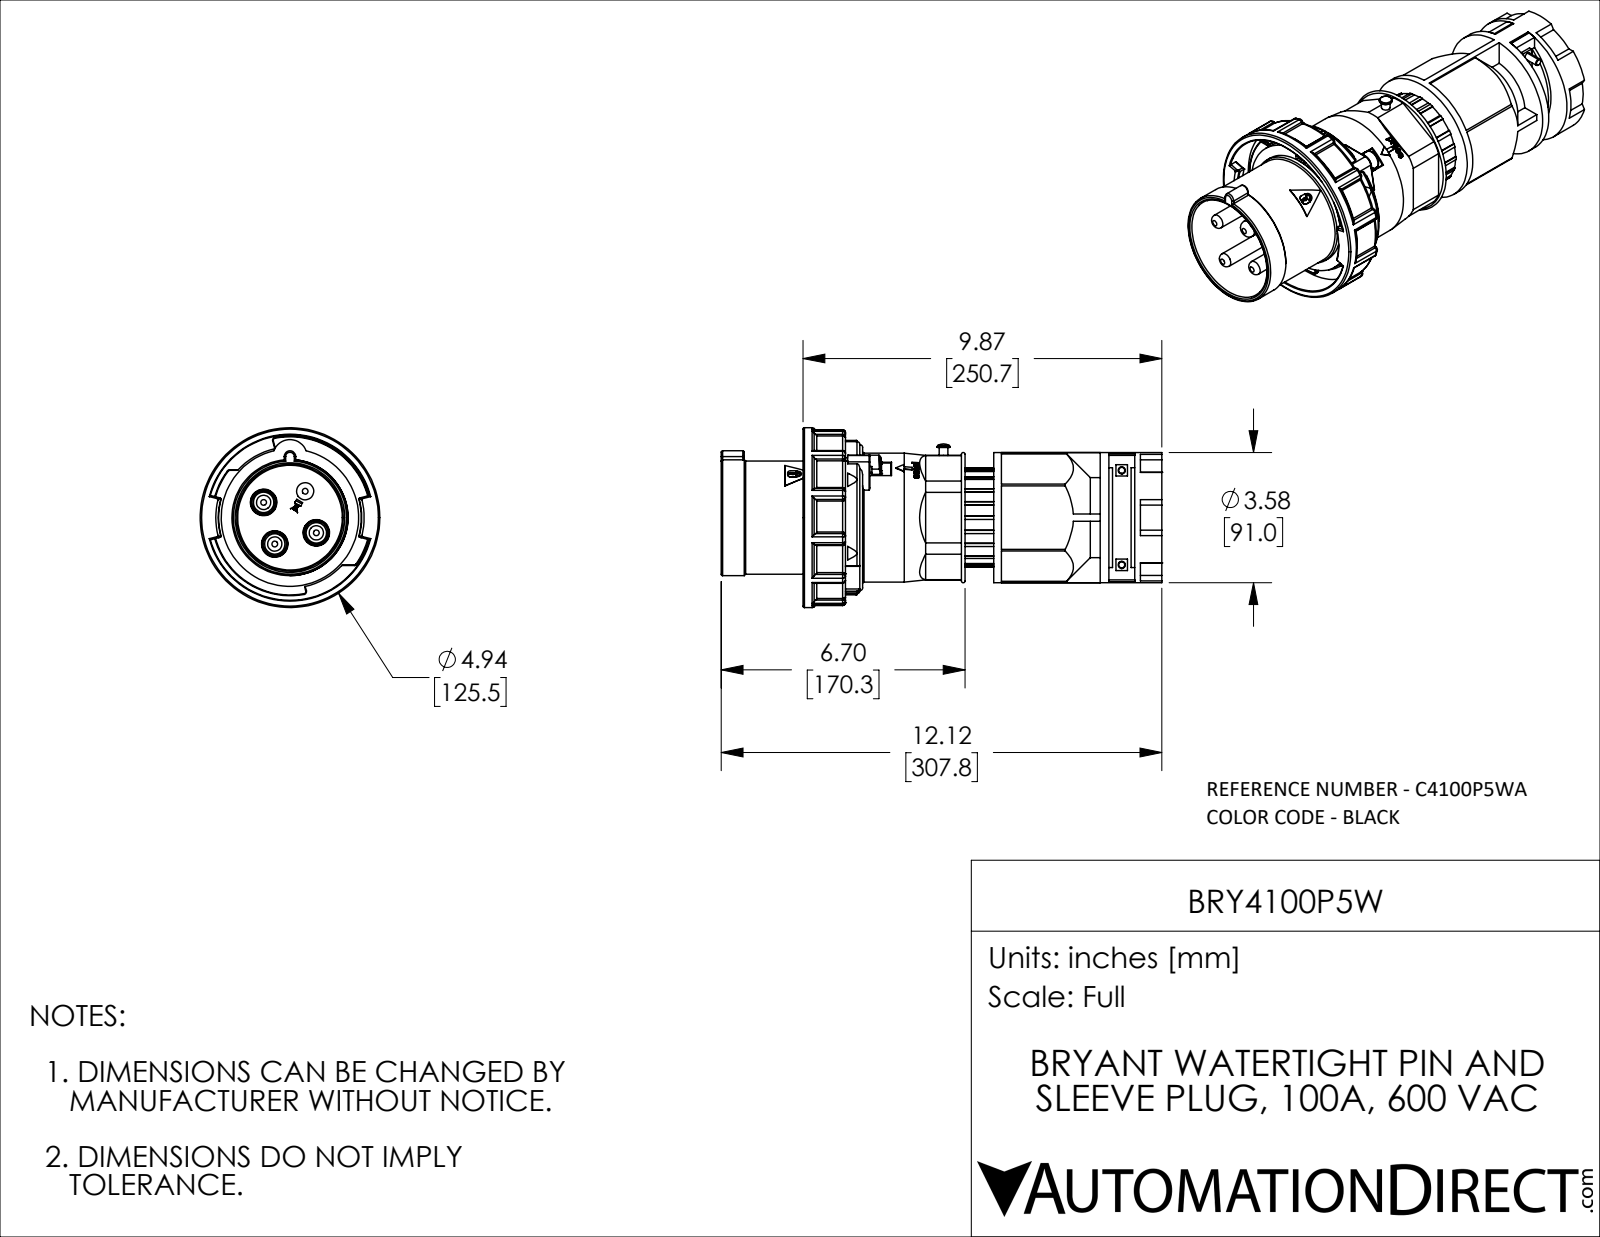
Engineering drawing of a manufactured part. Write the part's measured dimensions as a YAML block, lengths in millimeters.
part_name: "BRY4100P5W"
step_written_by: "SolidWorks 2021 (CONFIG_CONTROL_DESIGN)"
units: millimeters
bodies: {solids: 6, faces: 1440, planar: 500, cylindrical: 461, other: 479}
overall_size: [307.75, 125.5, 125.5]
volume: 1150000
surface_area: 213733
round_holes:
  - {diameter: 0.51, count: 1}
  - {diameter: 50, count: 1}
  - {diameter: 81, count: 1}
  - {diameter: 115.5, count: 1}
round_bosses_or_shafts:
  - {diameter: 10, count: 3}
  - {diameter: 5, count: 2}
  - {diameter: 125.5, count: 1}
  - {diameter: 96, count: 1}
  - {diameter: 91, count: 1}
  - {diameter: 90, count: 1}
  - {diameter: 81.1, count: 1}
  - {diameter: 79, count: 1}
partial_cylinders:
  - {radius: 2, count: 52}
  - {radius: 1, count: 46}
  - {radius: 0.5, count: 19}
  - {radius: 2.5, count: 6}
  - {radius: 0.2, count: 2}
  - {radius: 0.9, count: 2}
  - {radius: 1.2, count: 2}
  - {radius: 1.75, count: 2}
face_to_face_distances: [79.5, 118.5, 18, 100.5, 2.5, 24, 27, 32.67, 46.83, 6]
hole_center_spacings: [10.27]
